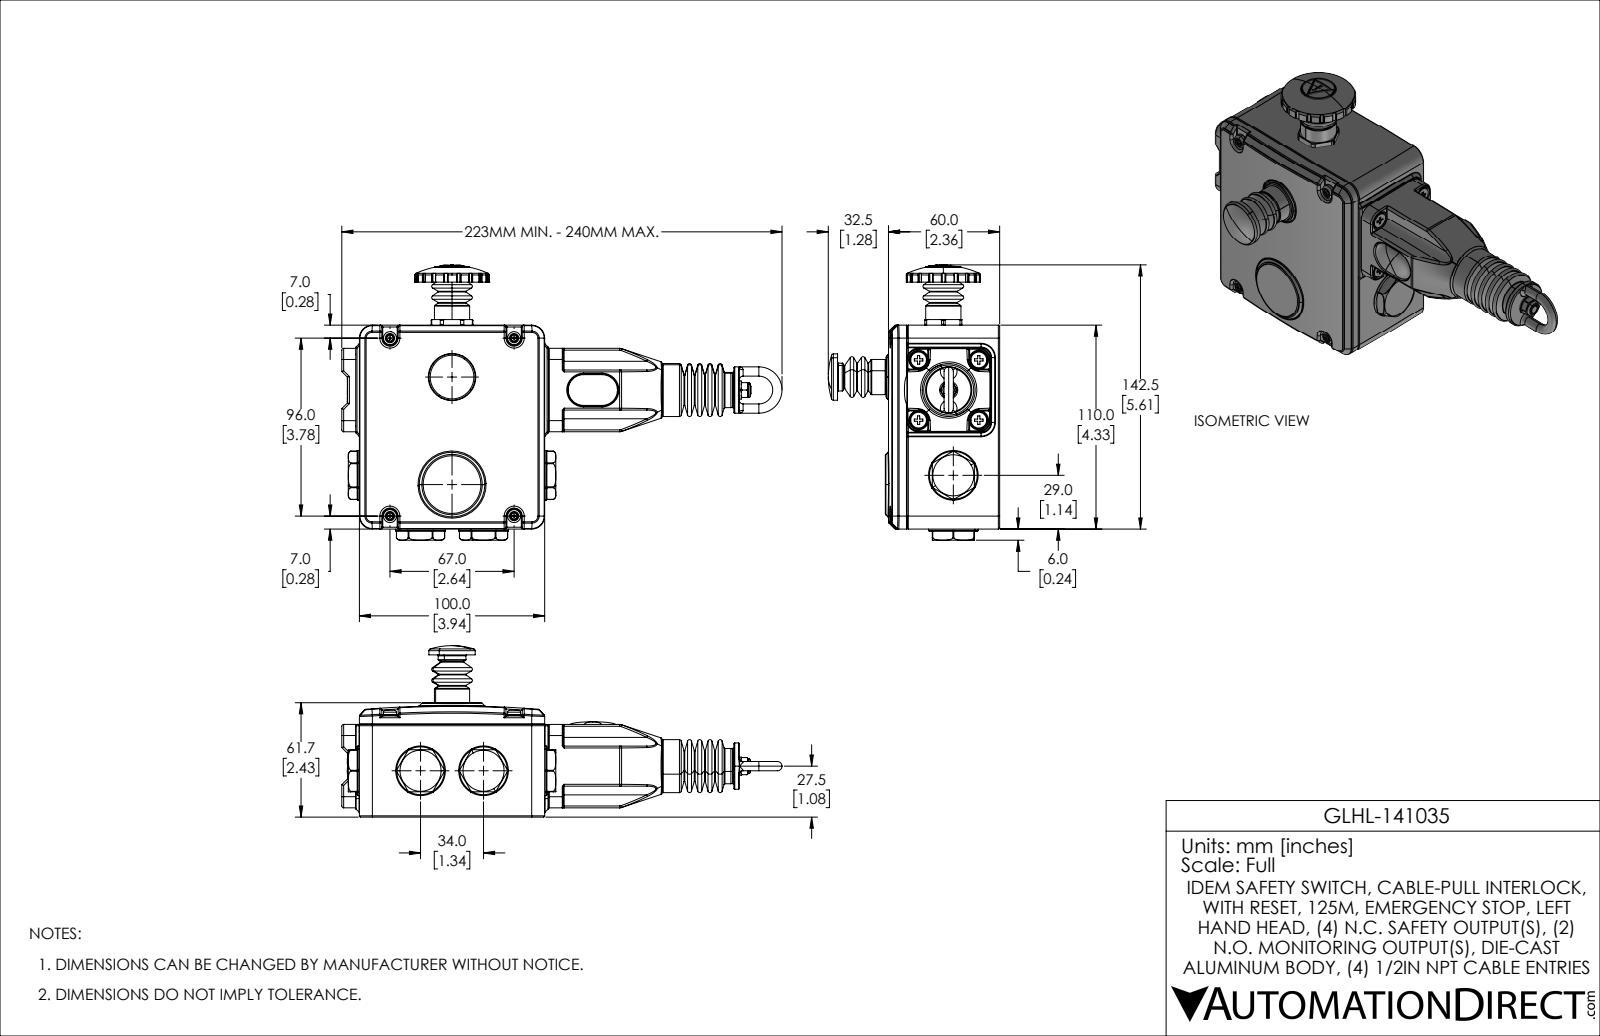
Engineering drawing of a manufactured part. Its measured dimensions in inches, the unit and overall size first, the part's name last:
Units: inches
Overall size (bounding box): 9.354 × 5.847 × 3.642
Round holes (diameter × count): ⌀0.197 ×11, ⌀0.209 ×9, ⌀0.374 ×7, ⌀0.354 ×6, ⌀0.13 ×4, ⌀0.157 ×4, ⌀0.189 ×4, ⌀0.213 ×4, ⌀0.228 ×4, ⌀0.118 ×3, ⌀0.173 ×3, ⌀0.504 ×3
Round bosses / shafts (diameter × count): ⌀0.335 ×7, ⌀0.236 ×7, ⌀0.173 ×7, ⌀0.197 ×6, ⌀0.276 ×5, ⌀0.138 ×4, ⌀0.051 ×4, ⌀1.055 ×3
Partial cylindrical surfaces — rounded edges, fillets, slot ends (radius × count): R0.02 ×226, R0.039 ×153, R0.008 ×136, R0.028 ×72, R0.012 ×20, R0.006 ×14, R0.236 ×12, R0.004 ×11
Main face-to-face distances: 0.138, 2.157, 0.114, 2.043, 4.331, 0.055, 0.157, 4.016, 3.878, 0.079
Hole centre spacings: 1.28, 0.374, 0.905, 1.891, 1.913, 3.012, 3.489, 3.78
Volume: 18.02 in³ · Surface area: 275.6 in²
Bodies: 32 solids, 4131 faces (1092 planar, 1370 cylindrical, 1669 other)
Part name (STEP PRODUCT): GLHL-141035
STEP written by: SolidWorks 2021 (AUTOMOTIVE_DESIGN)
